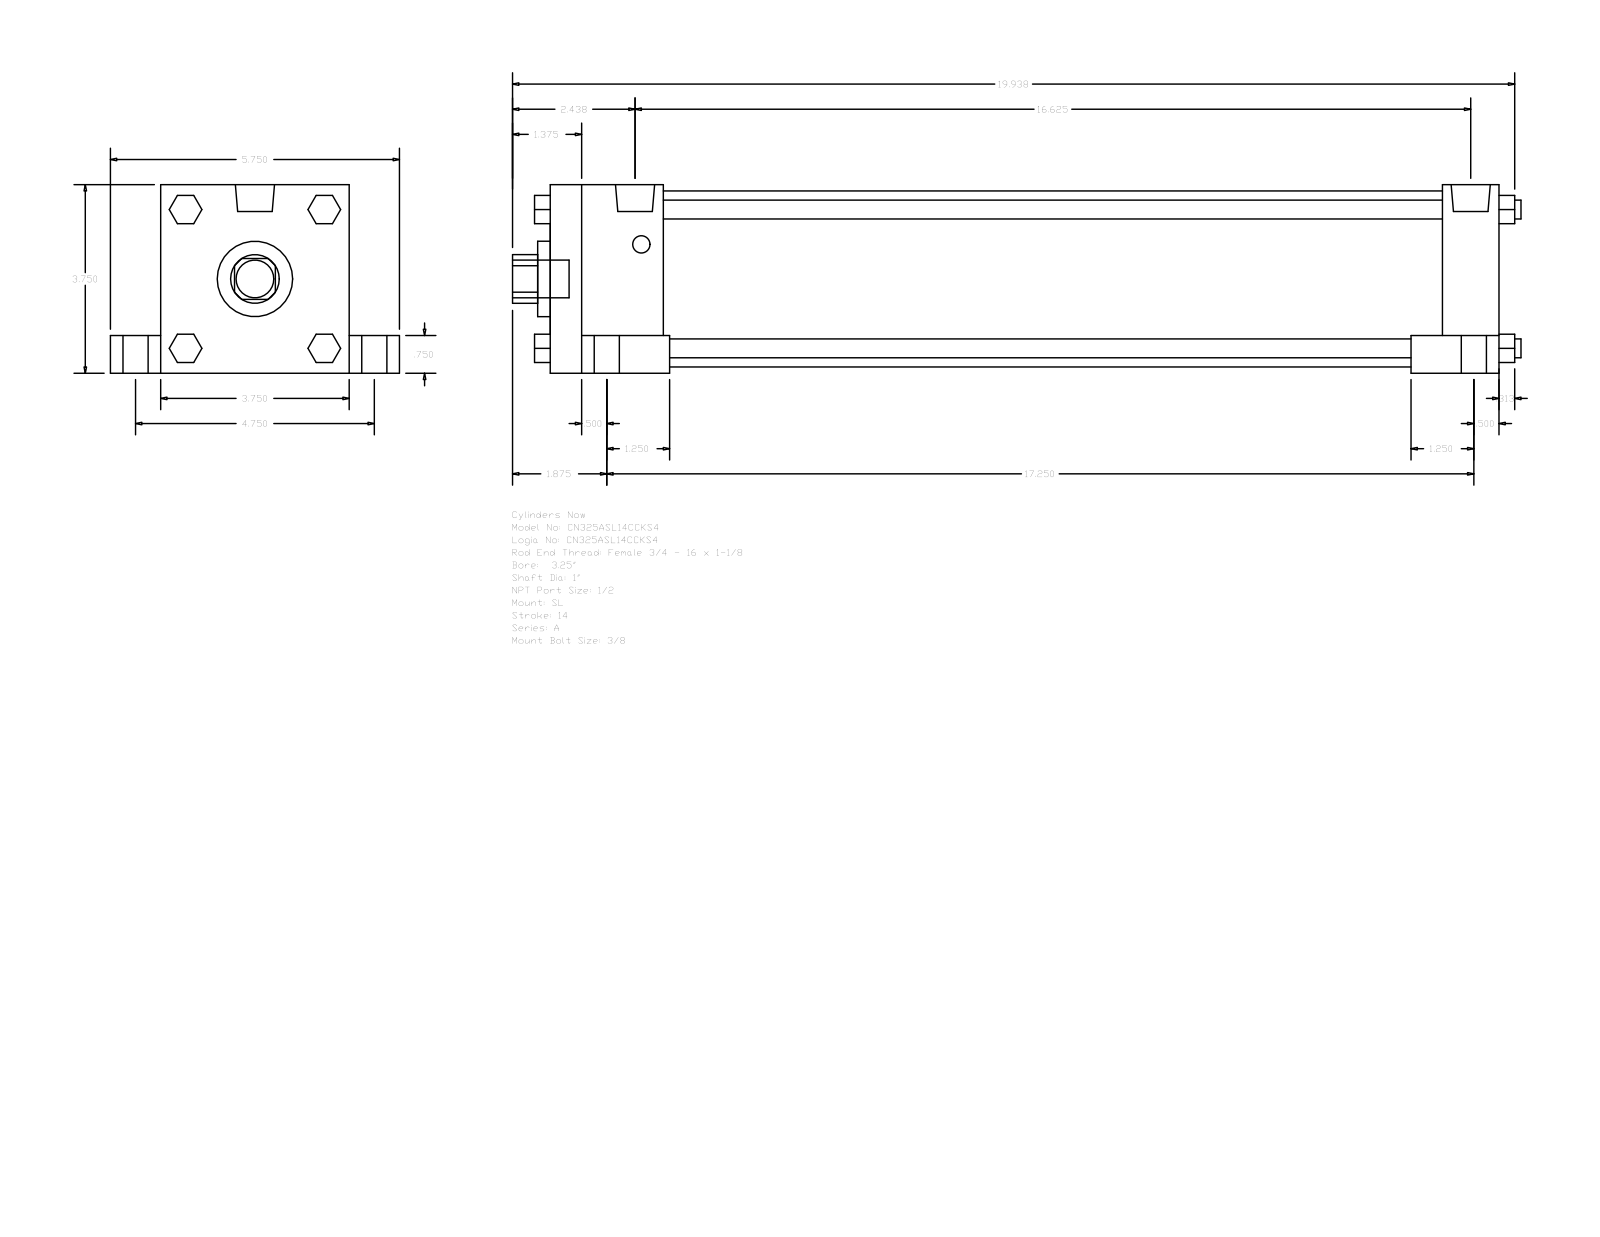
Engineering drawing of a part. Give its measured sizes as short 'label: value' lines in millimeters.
name: A_SL__0325_1
written by: GSSL Pune (CONFIG_CONTROL_DESIGN)
unit: mm
bodies: 0 solids, 150 faces (114 planar, 36 cylindrical, 0 other)
size: 509.59 × 146.05 × 95.25
holes: 1× ⌀25.4, 1× ⌀38.1, 1× ⌀88.9
bosses: 5× ⌀19.05, 4× ⌀12.7, 4× ⌀9.53, 4× ⌀8.73, 2× ⌀19.77
rounds: 1× R12.29
face distances: 95.24, 479.43, 19.05, 25.41, 120.65, 76.19, 57.15, 450.85, 393.7, 422.28
